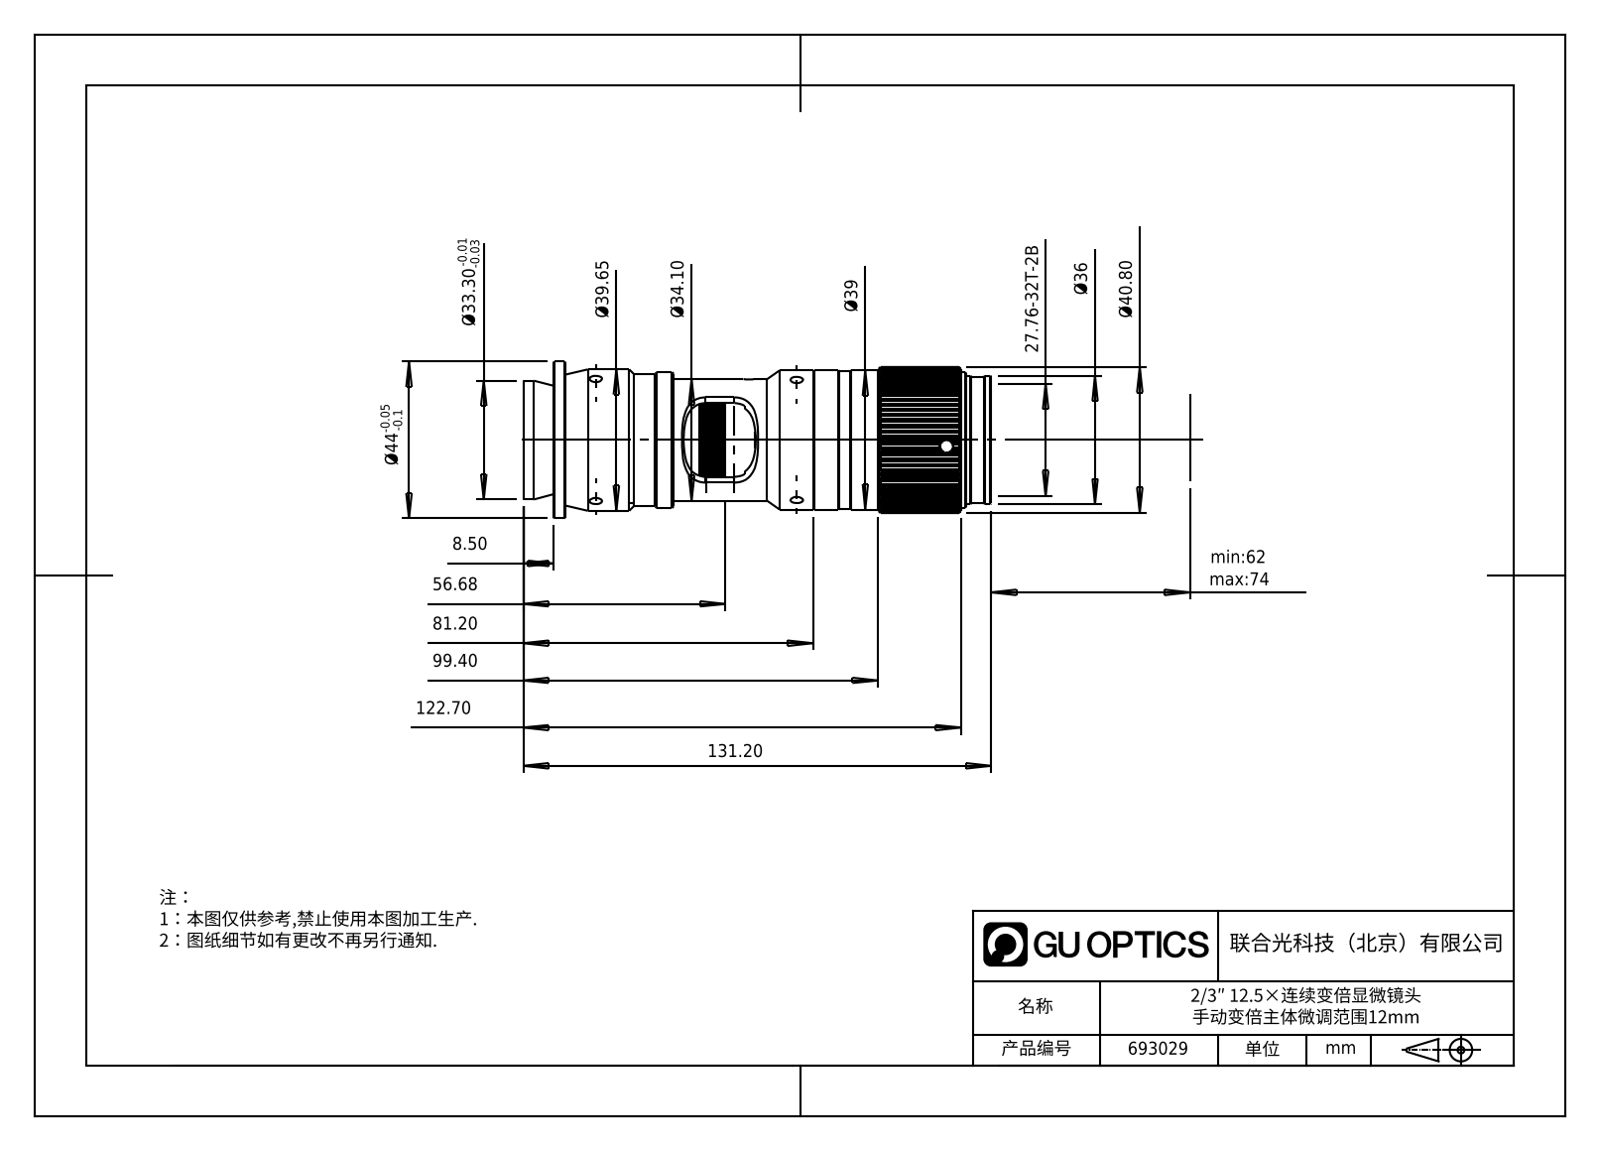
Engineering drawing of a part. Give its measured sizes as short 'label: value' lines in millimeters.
name: 693029
written by: SolidWorks 2020 (CONFIG_CONTROL_DESIGN)
unit: mm
bodies: 12 solids, 996 faces (579 planar, 316 cylindrical, 101 other)
size: 131.2 × 48.66 × 44
volume: 58 778 mm³; area: 59 247 mm²
holes: 6× ⌀3.5, 4× ⌀1.6, 3× ⌀0.95, 3× ⌀1.5, 3× ⌀3, 2× ⌀1.1, 1× ⌀2.2, 1× ⌀3.05, 1× ⌀4, 1× ⌀20.5, 1× ⌀21.6, 1× ⌀22.5
bosses: 3× ⌀2.2, 3× ⌀1.2, 1× ⌀44, 1× ⌀39.65, 1× ⌀39, 1× ⌀38.4, 1× ⌀38.1, 1× ⌀38
rounds: 6× R1.25, 4× R7, 1× R2, 1× R15.65, 1× R20.4
face distances: 1, 91.2, 3.3, 87.9, 72.7, 69.4, 18.5, 92.2, 88.9, 19.5
hole spacings: 18.1, 56.35, 31.35, 31.36, 48.5
